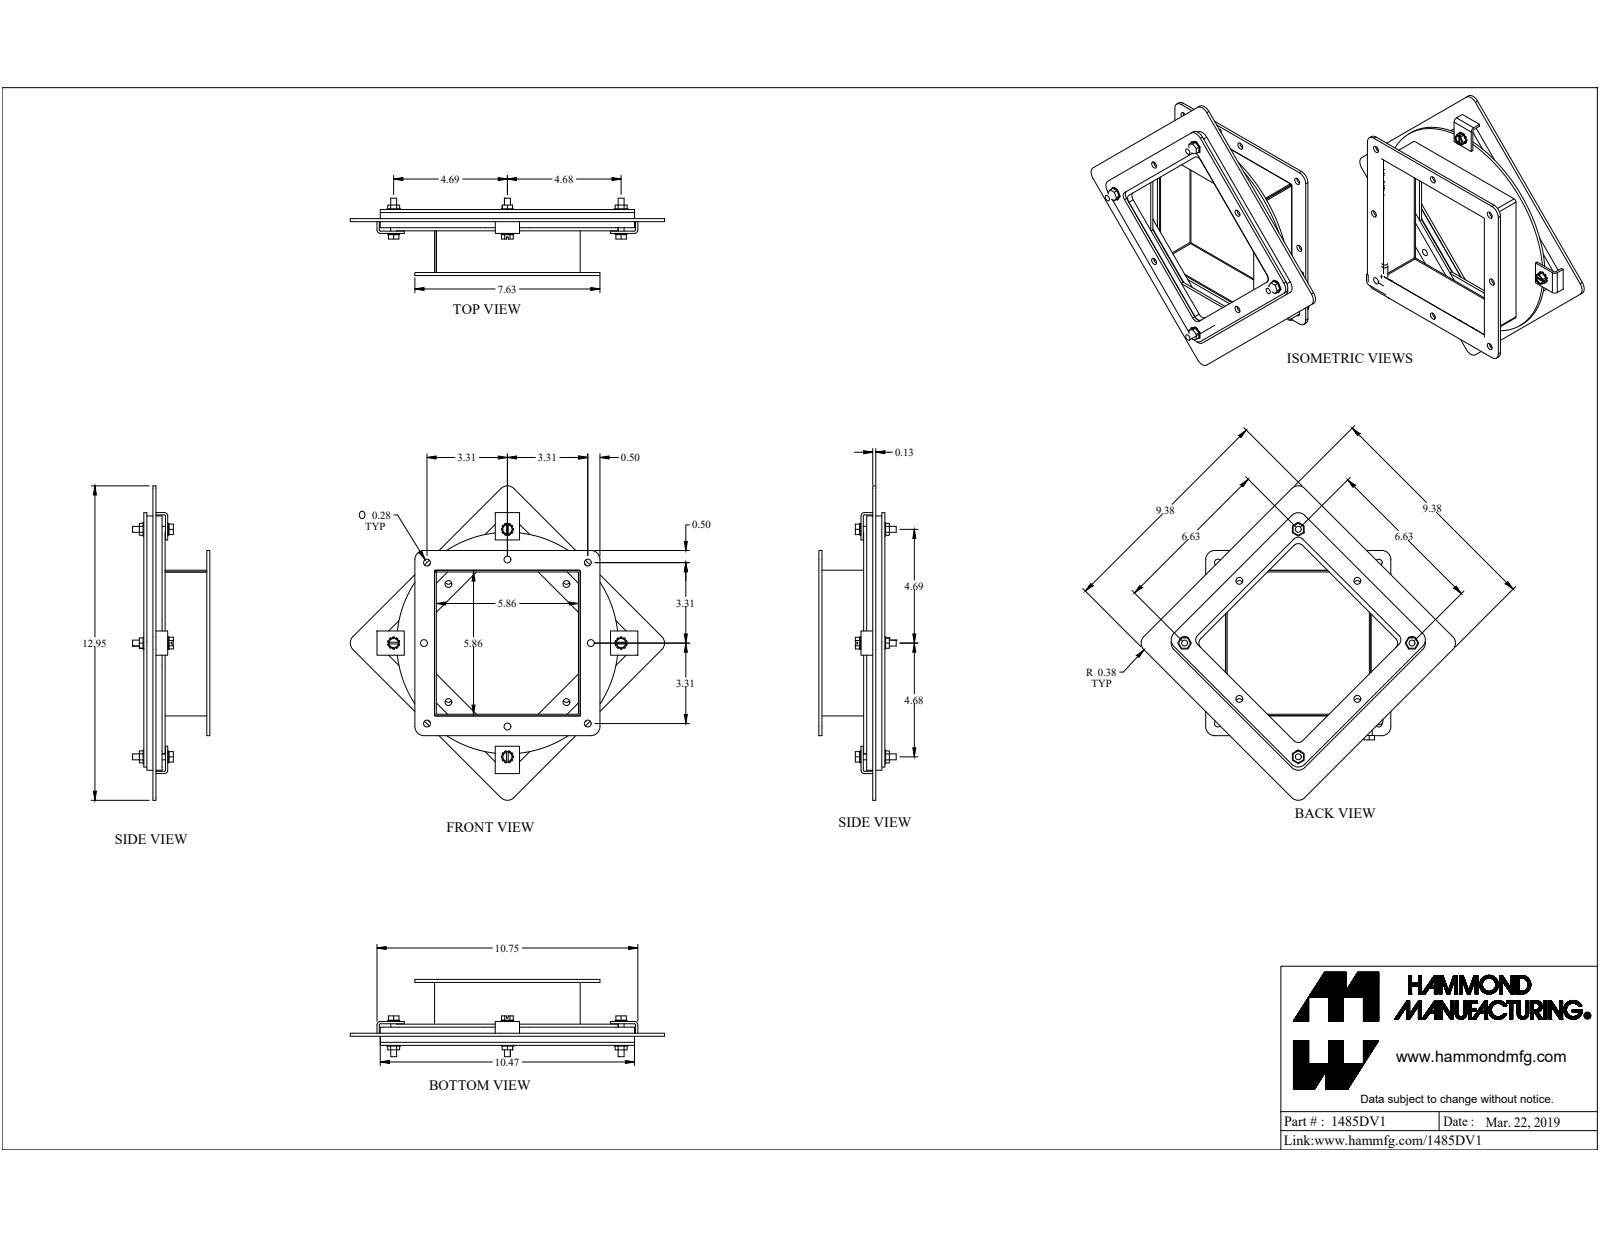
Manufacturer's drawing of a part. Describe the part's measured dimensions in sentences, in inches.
The part is named "1485DV1". Its 3-D file was written by "SolidWorks 2019 (CONFIG_CONTROL_DESIGN)". It is 41 solids with 785 faces: 542 planar, 218 cylindrical and 25 other. Overall it measures 12.948 by 12.948 by 3.434 inches. Its volume is 44 cubic inches and its surface area 674.7 square inches. Round holes: 16 of diameter 0.281, 6 of diameter 0.375, 5 of diameter 0.196, 5 of diameter 0.258, 4 of diameter 0.312, 2 of diameter 0.187, 2 of diameter 0.265, 2 of diameter 0.313, 1 of diameter 0.224, 1 of diameter 0.35. Round bosses or shafts: 5 of diameter 0.244, 3 of diameter 0.25, 2 of diameter 0.563, 1 of diameter 9.125, 1 of diameter 0.52, 1 of diameter 0.455, 1 of diameter 0.246. Partial cylindrical surfaces (rounded edges, fillets, slot ends): 17 of radius 0.25, 12 of radius 0.375, 9 of radius 0.048, 9 of radius 0.143, 4 of radius 0.062, 3 of radius 0.036, 3 of radius 0.108, 1 of radius 0.06. The main face-to-face distances are 0.25, 0.375, 2.593, 0.125, 0.125, 0.375, 2.218, 1.843, 0.5, 0.75. The hole center spacings are 3.315, 7.519, 4.861, 5.81, 5.811, 6.615, 6.625, 2.631.
